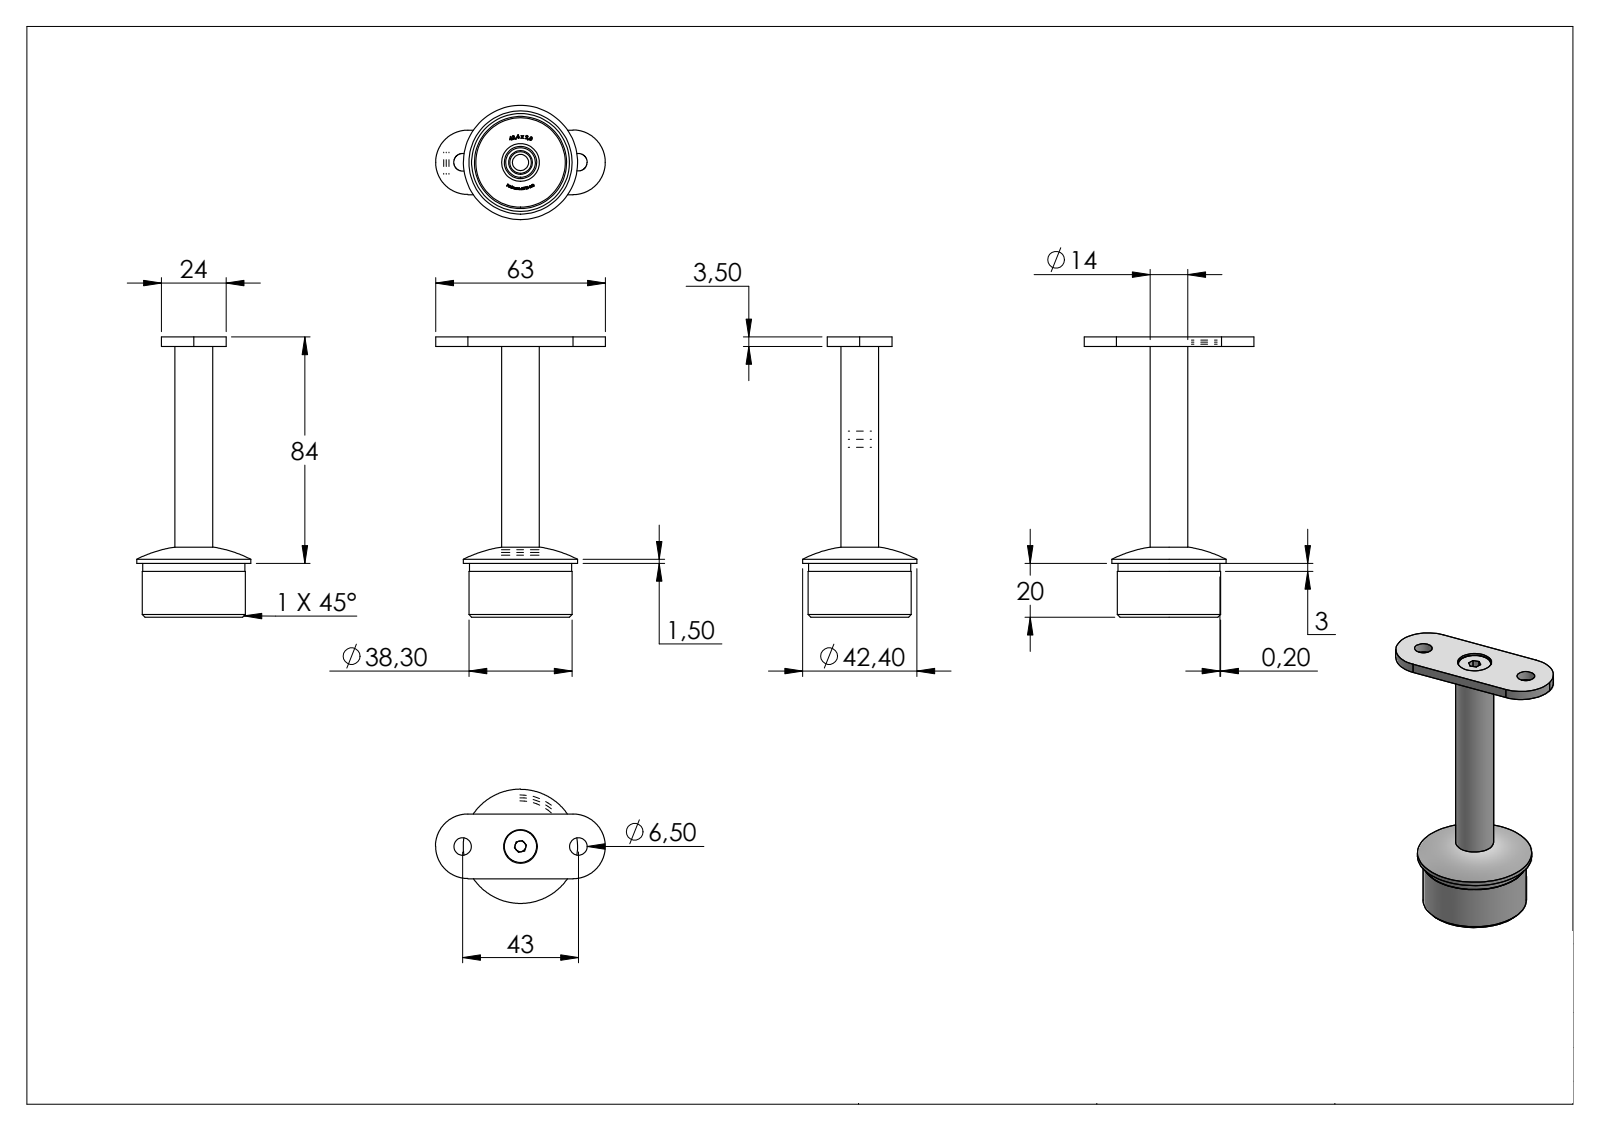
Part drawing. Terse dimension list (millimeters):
name: 60180-240; DIN-7991_-_DIN7991 M6x16_DIN7991 M6x16; 60721-240; DIN-7991_-_DIN7991 M6x16 (+5 more)
written by: SolidWorks 2018 (CONFIG_CONTROL_DESIGN)
unit: mm
bodies: 4 solids, 371 faces (221 planar, 20 cylindrical, 130 other)
size: 105.68 × 63 × 42.4
volume: 26 724 mm³; area: 16 290 mm²
holes: 2× ⌀6.5, 1× ⌀5, 1× ⌀6.8, 1× ⌀12.5, 1× ⌀14.2, 1× ⌀34.2
bosses: 1× ⌀42.4, 1× ⌀38.3, 1× ⌀37.9, 1× ⌀14, 1× ⌀12, 1× ⌀8, 1× ⌀6
rounds: 2× R12
face distances: 3.5, 83.53, 80.03, 0.5, 80.53, 84.03, 3, 81.03, 24, 20
hole spacings: 21.5, 43
